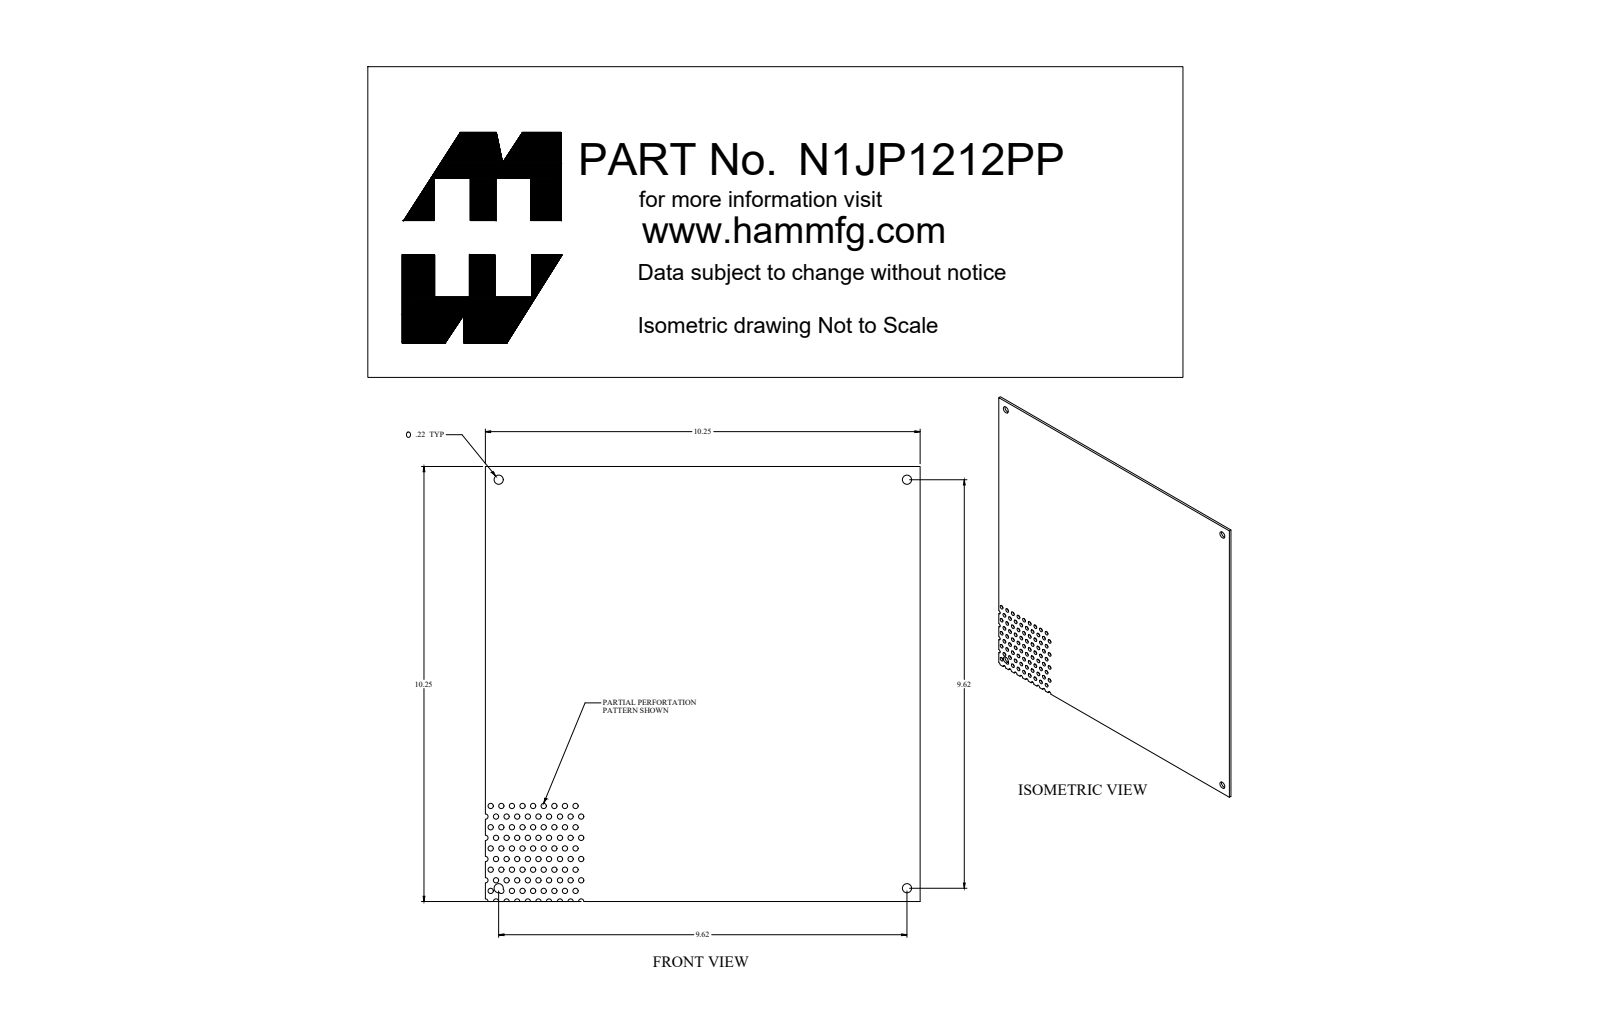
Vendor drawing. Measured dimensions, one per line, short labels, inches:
name: N1JP1212PP
written by: SolidWorks 2018 (AUTOMOTIVE_DESIGN)
unit: in
bodies: 1 solid, 203 faces (19 planar, 184 cylindrical, 0 other)
size: 10.25 × 10.25 × 0.072
volume: 7.477 in³; area: 213.2 in²
holes: 75× ⌀0.125, 5× ⌀0.125, 4× ⌀0.218
rounds: 10× R0.063, 5× R0.062
face distances: 0.072, 10.25
hole spacings: 0.5, 0.28, 0.25, 0.559, 0.707, 0.75, 0.45, 0.673
